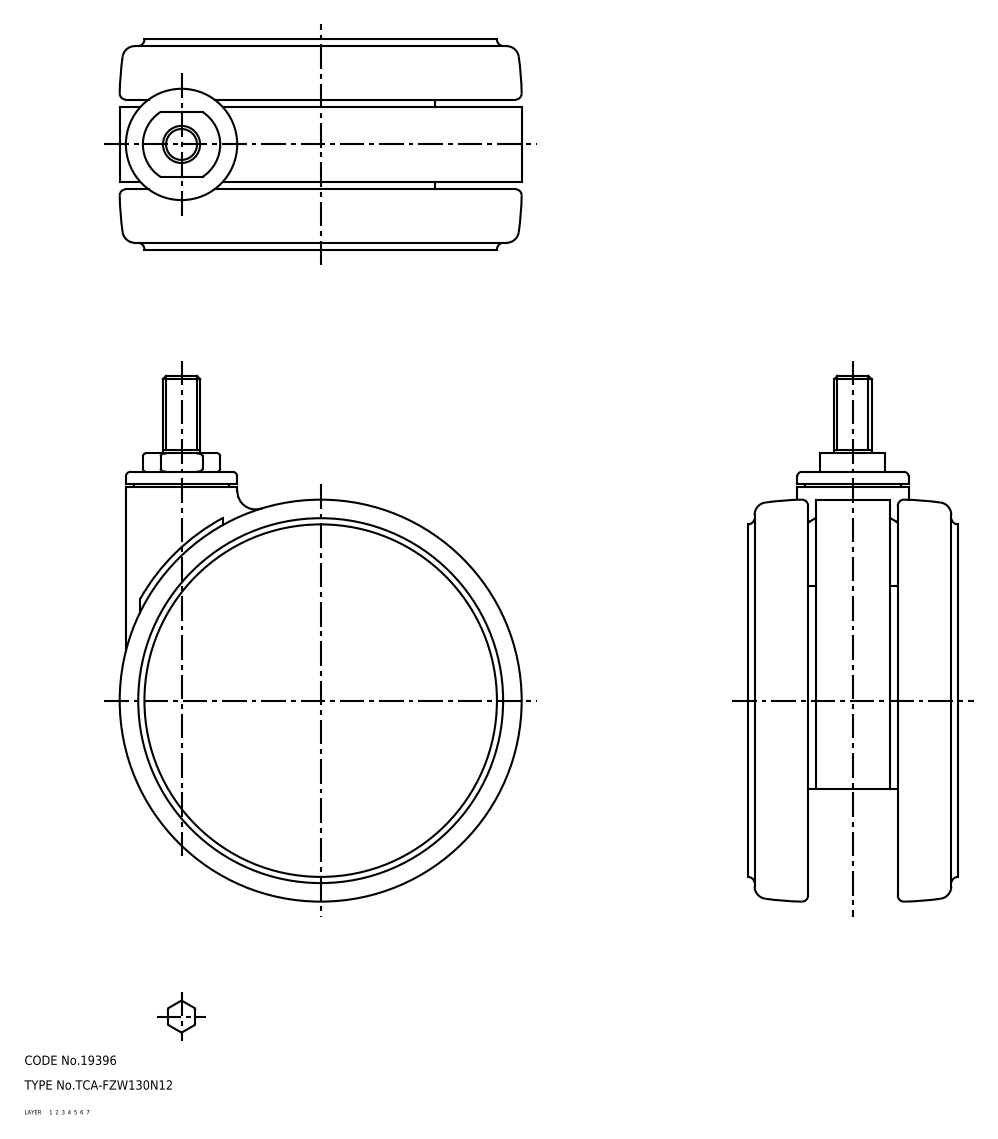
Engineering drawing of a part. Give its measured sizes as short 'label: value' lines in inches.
name: TCA-FZW130N12; caster
written by: SolidWorks 2015 (AUTOMOTIVE_DESIGN)
unit: in
bodies: 1 solid, 2279 faces (644 planar, 943 cylindrical, 692 other)
size: 6.693 × 5.118 × 2.685
volume: 29.74 in³; area: 291.7 in²
holes: 1× ⌀0.394, 1× ⌀0.398, 1× ⌀0.413, 1× ⌀0.472, 1× ⌀0.591, 1× ⌀0.598, 1× ⌀0.622, 1× ⌀0.63, 1× ⌀0.756, 1× ⌀1.024, 1× ⌀1.11, 1× ⌀1.181
bosses: 1× ⌀4.638, 1× ⌀4.488, 1× ⌀1.654, 1× ⌀1.417, 1× ⌀1.22, 1× ⌀1.098, 1× ⌀1.087, 1× ⌀0.748
rounds: 201× R0.059, 98× R0.039, 78× R0.02, 44× R0.012, 16× R0.008, 16× R0.118, 1× R0.079, 1× R0.276
face distances: 0.079, 2.606, 0.071, 0.15, 2.457, 2.535, 0.295, 0.445, 2.24, 0.366
